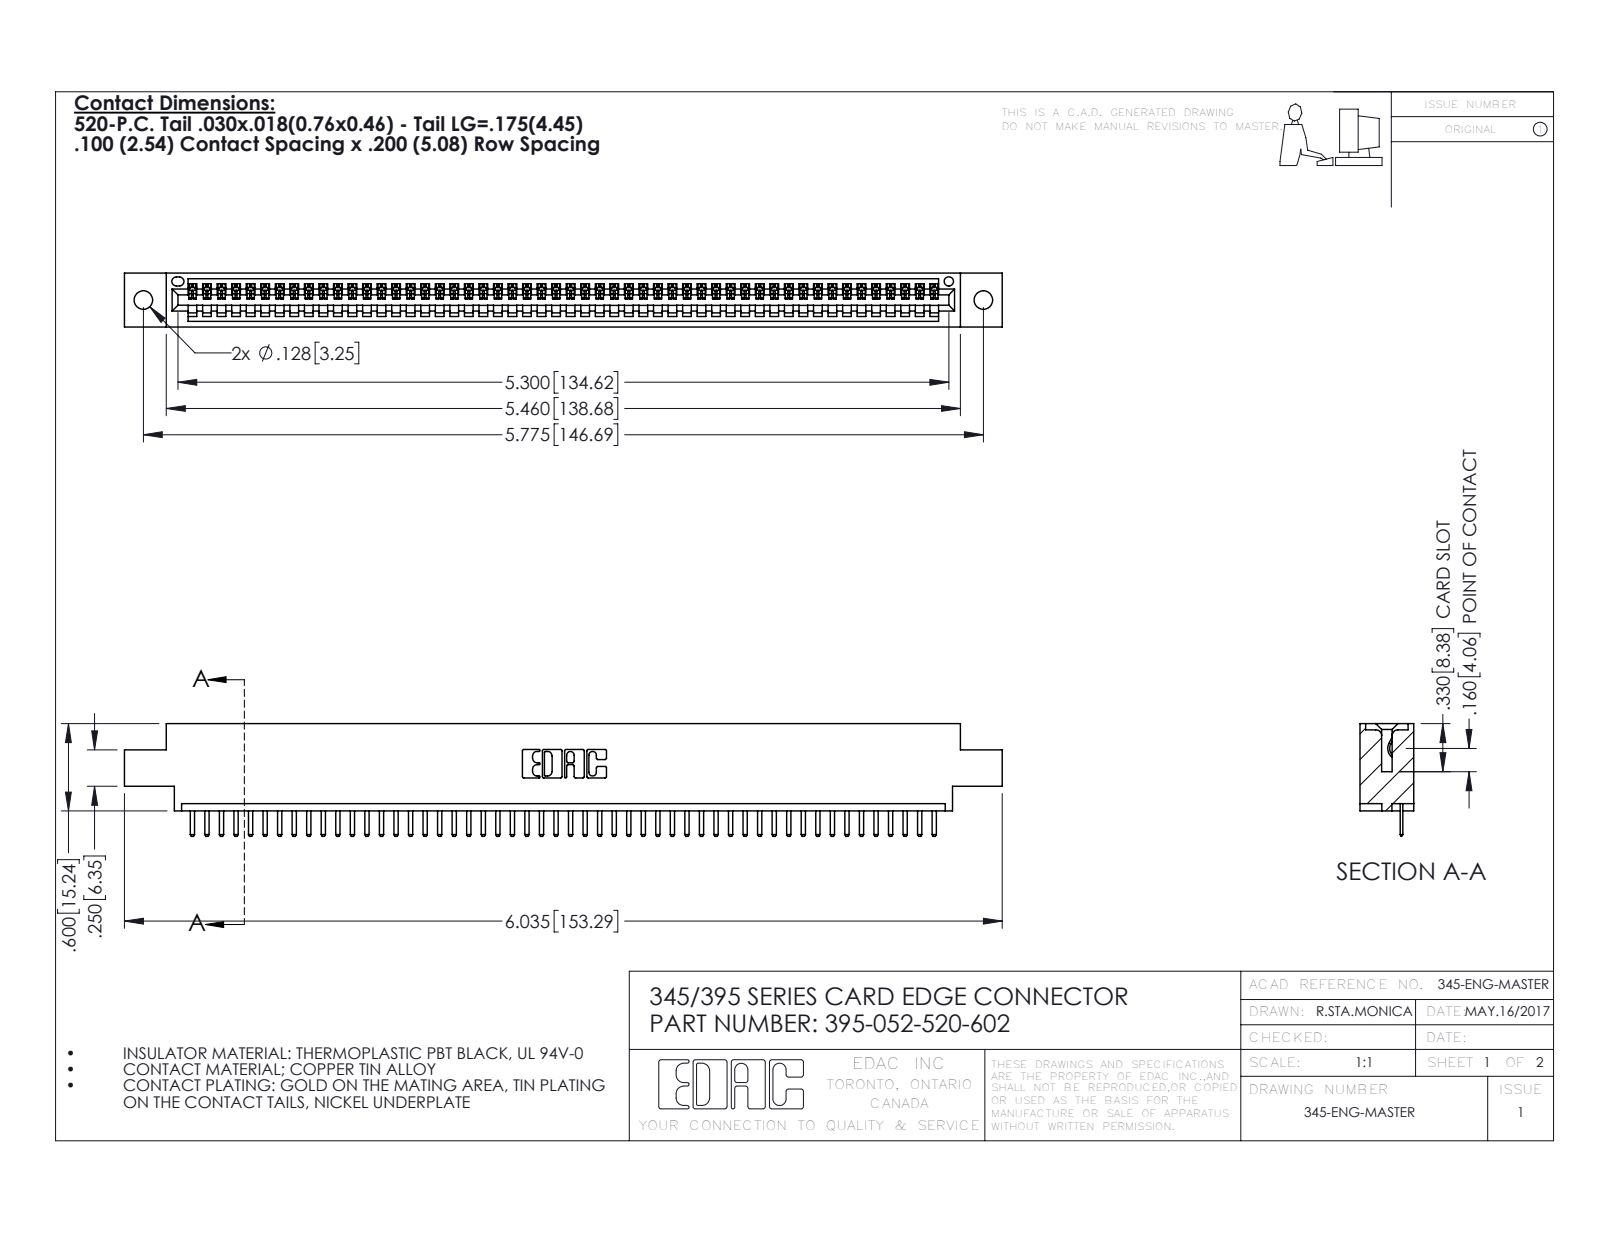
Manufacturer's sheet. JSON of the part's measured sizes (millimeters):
{"part_name": "395-052-520-602; 345-292-001_345-293-120; 345 Part_0.170 Offset - 0.128 Dia", "step_written_by": "SolidWorks 2016 (CONFIG_CONTROL_DESIGN)", "units": "millimeters", "bodies": {"solids": 53, "faces": 3354, "planar": 2268, "cylindrical": 1086, "other": 0}, "overall_size": [153.3, 19.7, 9.4], "volume_mm3": 14300, "surface_area_mm2": 18560, "round_holes": [[3.3, 2], [1.6, 1]], "partial_cylinders_radius": [[0.3, 106], [0.2, 104], [0.3, 22], [0.2, 6], [0.8, 6], [0.7, 3], [0.8, 2], [1, 2]], "face_to_face_distances": [7.6, 1.8, 9.4, 5.1, 2.5, 6.9, 0.6, 5.7, 1.8, 4.4], "hole_center_spacings": [6.9, 140.7, 146.7]}
